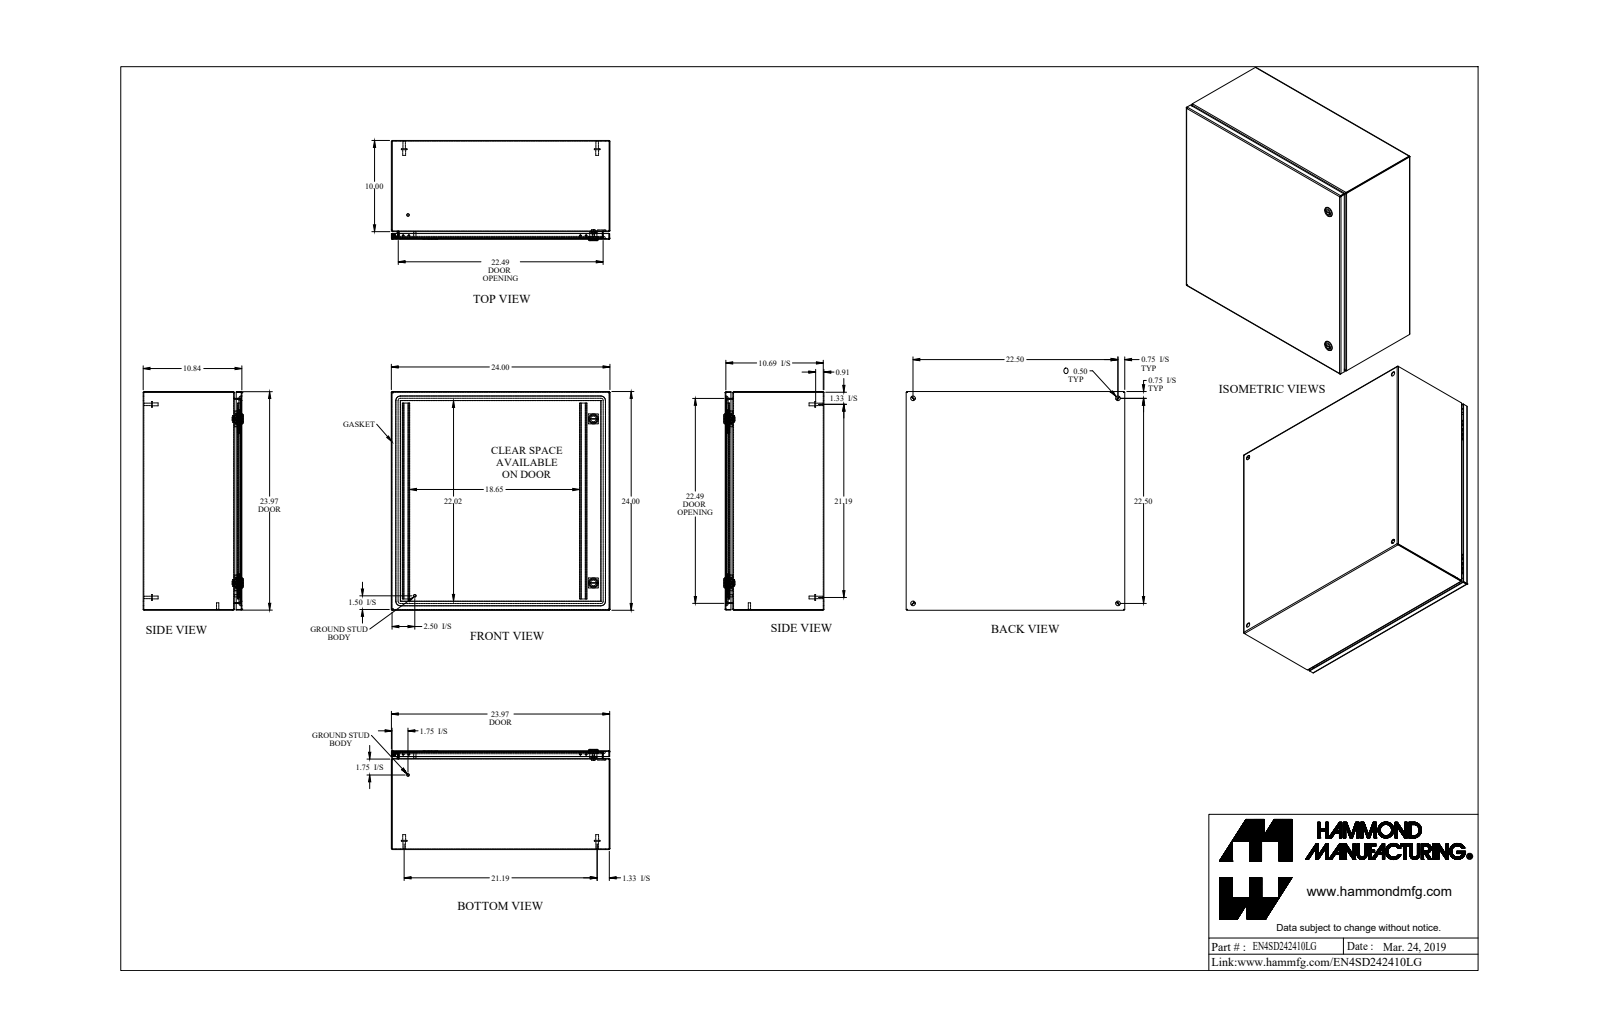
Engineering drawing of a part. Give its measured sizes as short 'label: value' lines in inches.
name: EN4SD242410LG
written by: SolidWorks 2019 (AUTOMOTIVE_DESIGN)
unit: in
bodies: 27 solids, 752 faces (359 planar, 257 cylindrical, 136 other)
size: 24 × 24 × 10.997
volume: 177.7 in³; area: 4 974 in²
holes: 4× ⌀0.5, 2× ⌀0.232, 2× ⌀0.625, 2× ⌀0.785, 1× ⌀0.172, 1× ⌀0.24, 1× ⌀0.242
bosses: 4× ⌀0.625, 4× ⌀0.313, 4× ⌀0.27, 2× ⌀1.1, 2× ⌀0.525, 2× ⌀0.281, 2× ⌀0.25, 1× ⌀0.455
rounds: 16× R0.036, 16× R0.108, 12× R0.043, 12× R0.081, 12× R0.382, 8× R0.1, 8× R19.003, 4× R0.006
face distances: 0.072, 10.765, 23.928, 10.693, 10.837, 23.856, 24, 0.837, 9.928, 0.75
hole spacings: 22.5, 31.82, 2.493, 2.494, 17.999, 20.277, 20.278, 21.544
